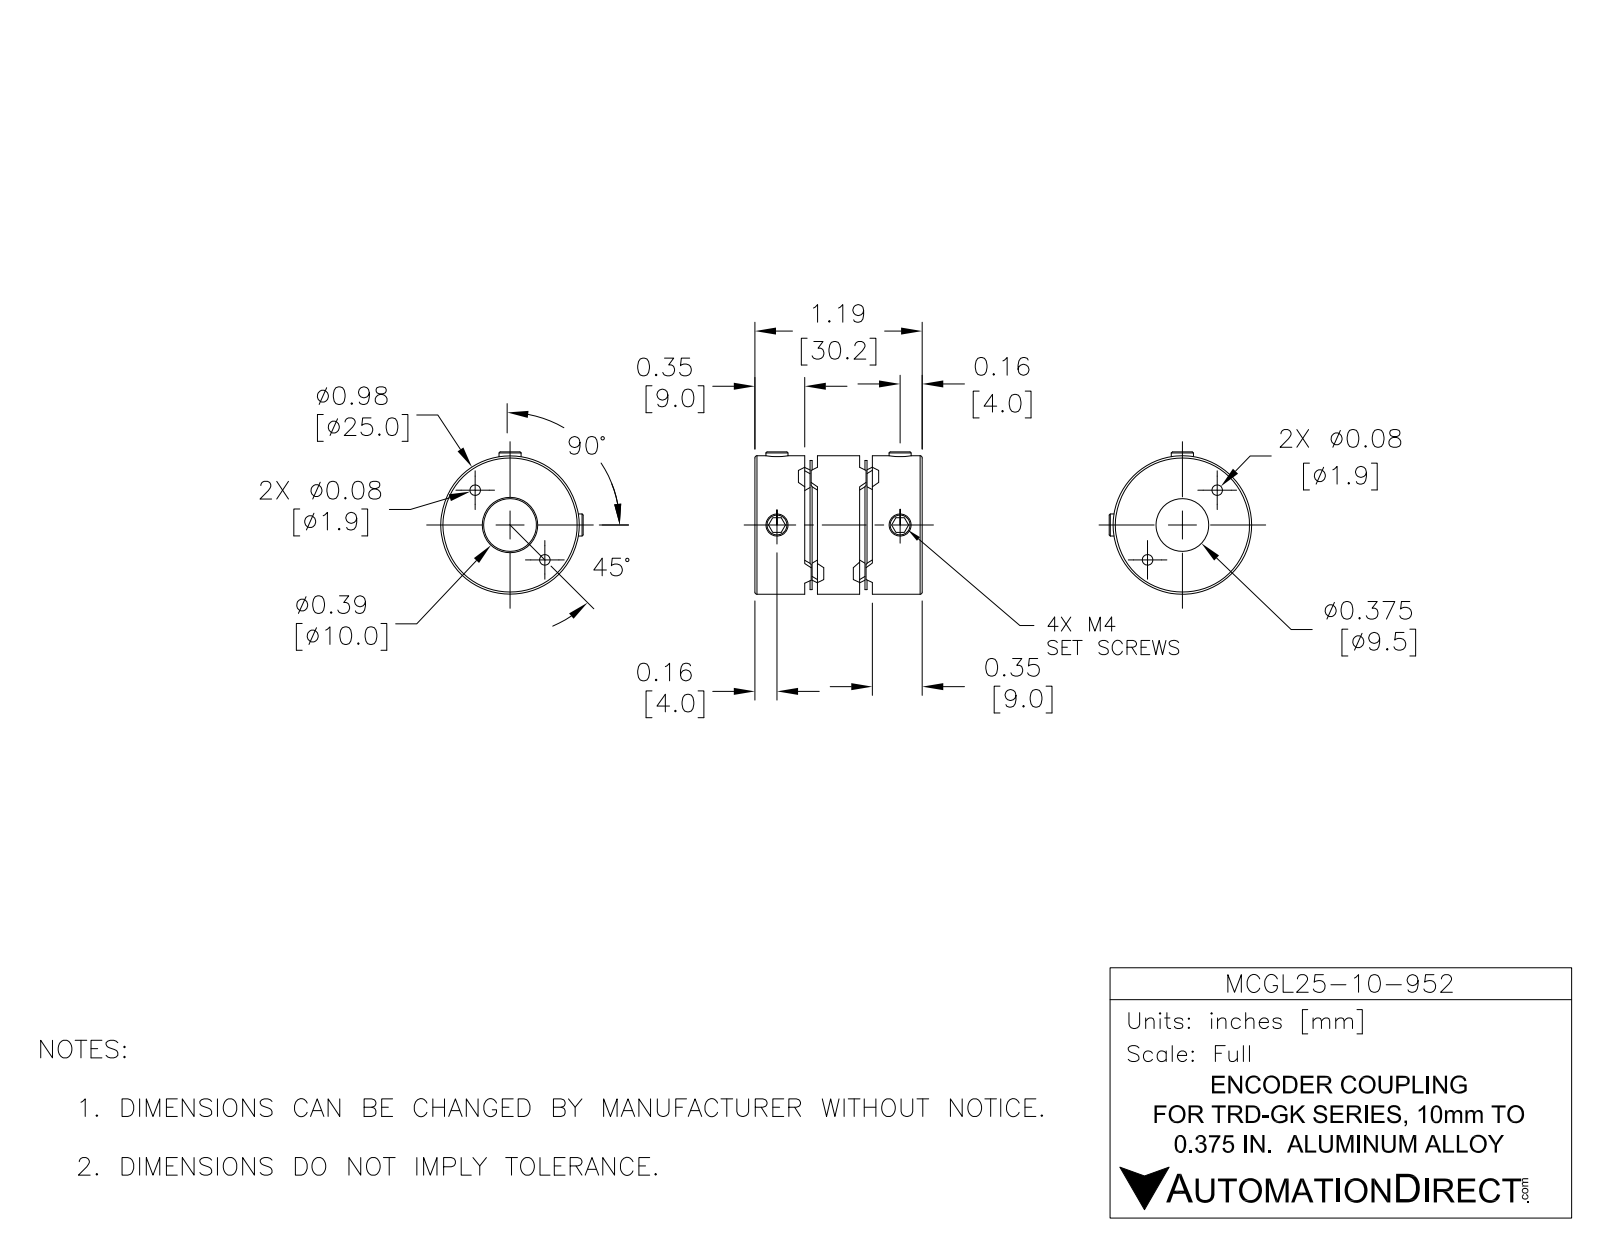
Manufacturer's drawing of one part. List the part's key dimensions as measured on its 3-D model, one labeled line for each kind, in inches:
Part name (STEP PRODUCT): MCGL25-10-952
STEP written by: SolidWorks 2016 (AUTOMOTIVE_DESIGN)
Units: inches
Bodies: 1 solid, 142 faces (70 planar, 36 cylindrical, 36 other)
Overall size (bounding box): 1.181 × 0.984 × 0.984
Volume: 0.591 in³ · Surface area: 10.93 in²
Round holes (diameter × count): ⌀0.157 ×4, ⌀0.142 ×2, ⌀0.375 ×1, ⌀0.394 ×1, ⌀0.472 ×1
Round bosses / shafts (diameter × count): ⌀0.984 ×1
Main face-to-face distances: 0.059, 0.413, 0.083, 0.331, 0.354, 0.496, 0.685, 0.437, 0.744, 0.248
Hole centre spacings: 0.37, 0.866, 0.74
